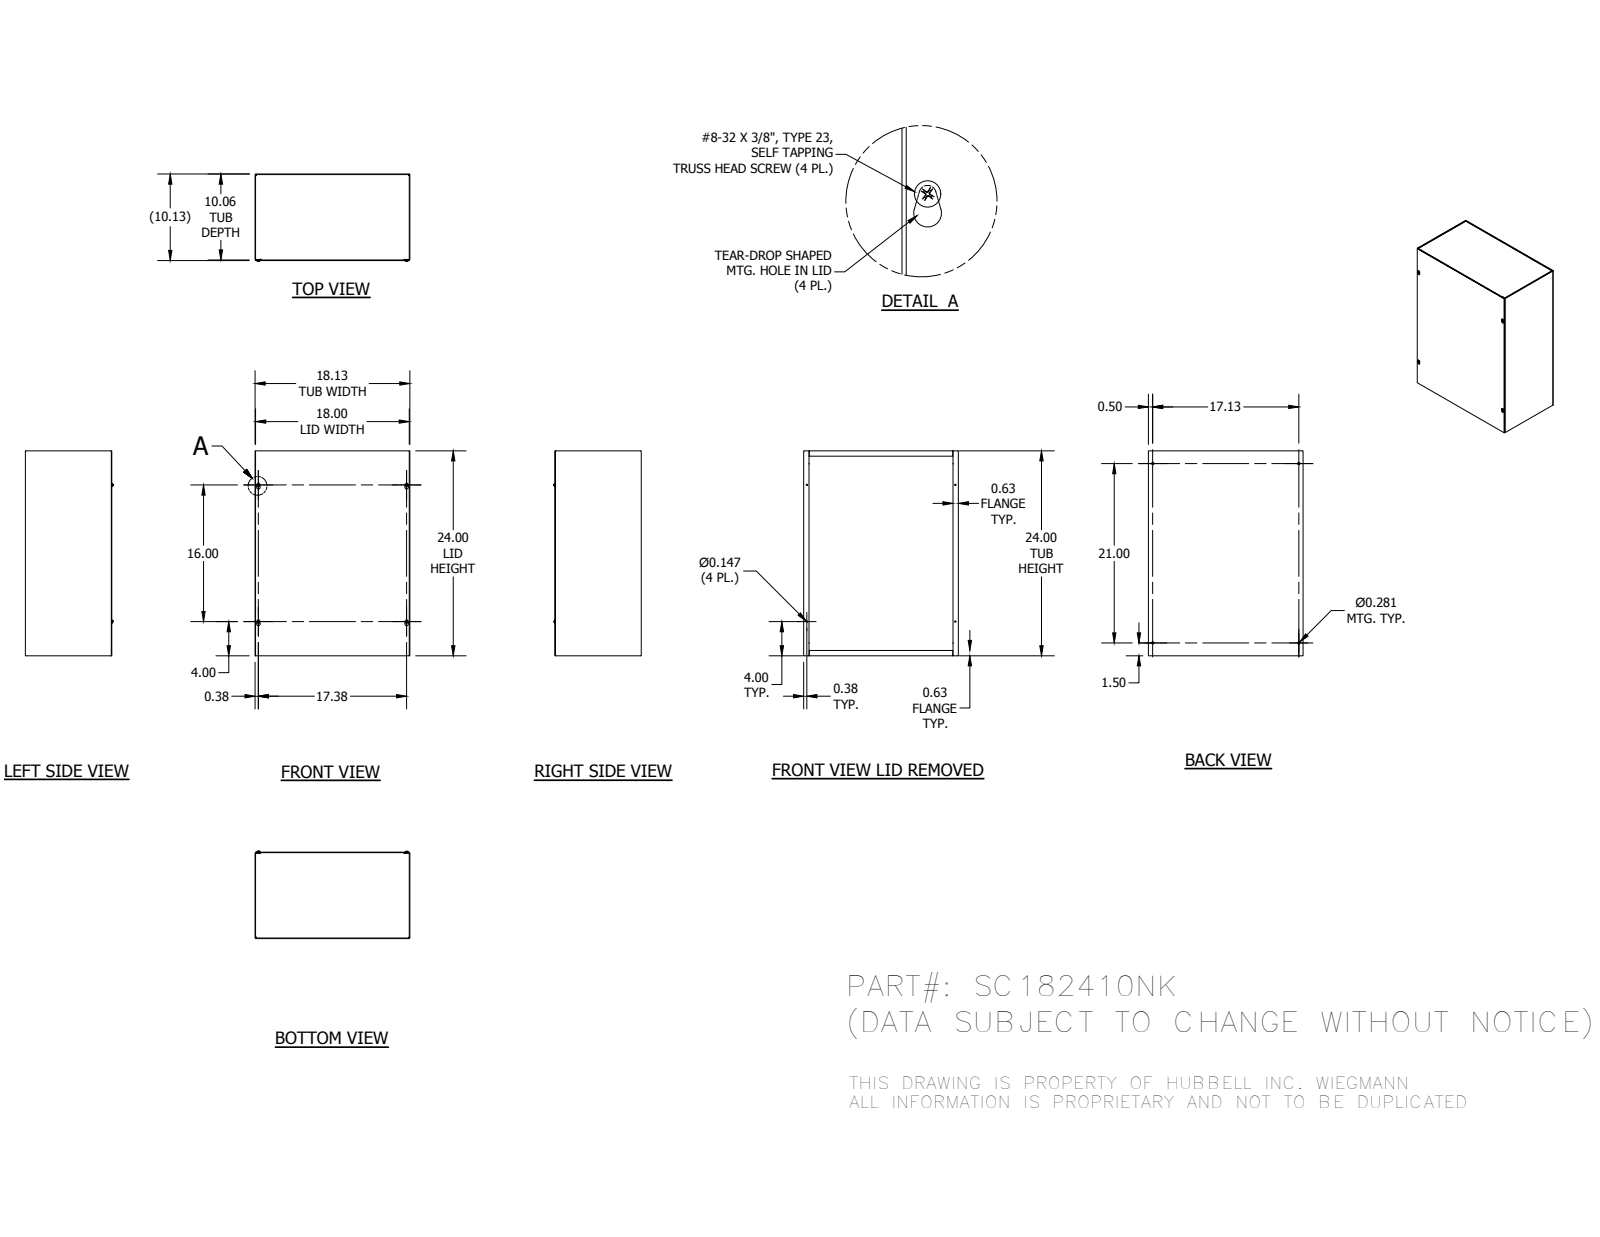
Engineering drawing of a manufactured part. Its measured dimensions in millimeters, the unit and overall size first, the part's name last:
Units: millimetres
Overall size (bounding box): 609.6 × 460.38 × 259.72
Round holes (diameter × count): ⌀3.73 ×4, ⌀7.14 ×4
Round bosses / shafts (diameter × count): ⌀9.75 ×4, ⌀4.17 ×4
Partial cylindrical surfaces — rounded edges, fillets, slot ends (radius × count): R0.79 ×12, R2.38 ×12, R3.17 ×4, R5.16 ×4
Main face-to-face distances: 1.59, 255.59, 254, 458.79, 257.18, 608.01, 457.2, 460.38, 609.6, 606.42
Hole centre spacings: 63.58, 442.73, 469.91, 642.48, 406.4, 434.98, 441.32, 533.4
Volume: 1 833 000 mm³ · Surface area: 2 323 000 mm²
Bodies: 8 solids, 268 faces (152 planar, 48 cylindrical, 68 other)
Part name (STEP PRODUCT): SC182410NKBLR; SC1810NKTB; SC1824LPA; 34056 (+1 more)
STEP written by: Autodesk Inventor 2014 (AUTOMOTIVE_DESIGN)
